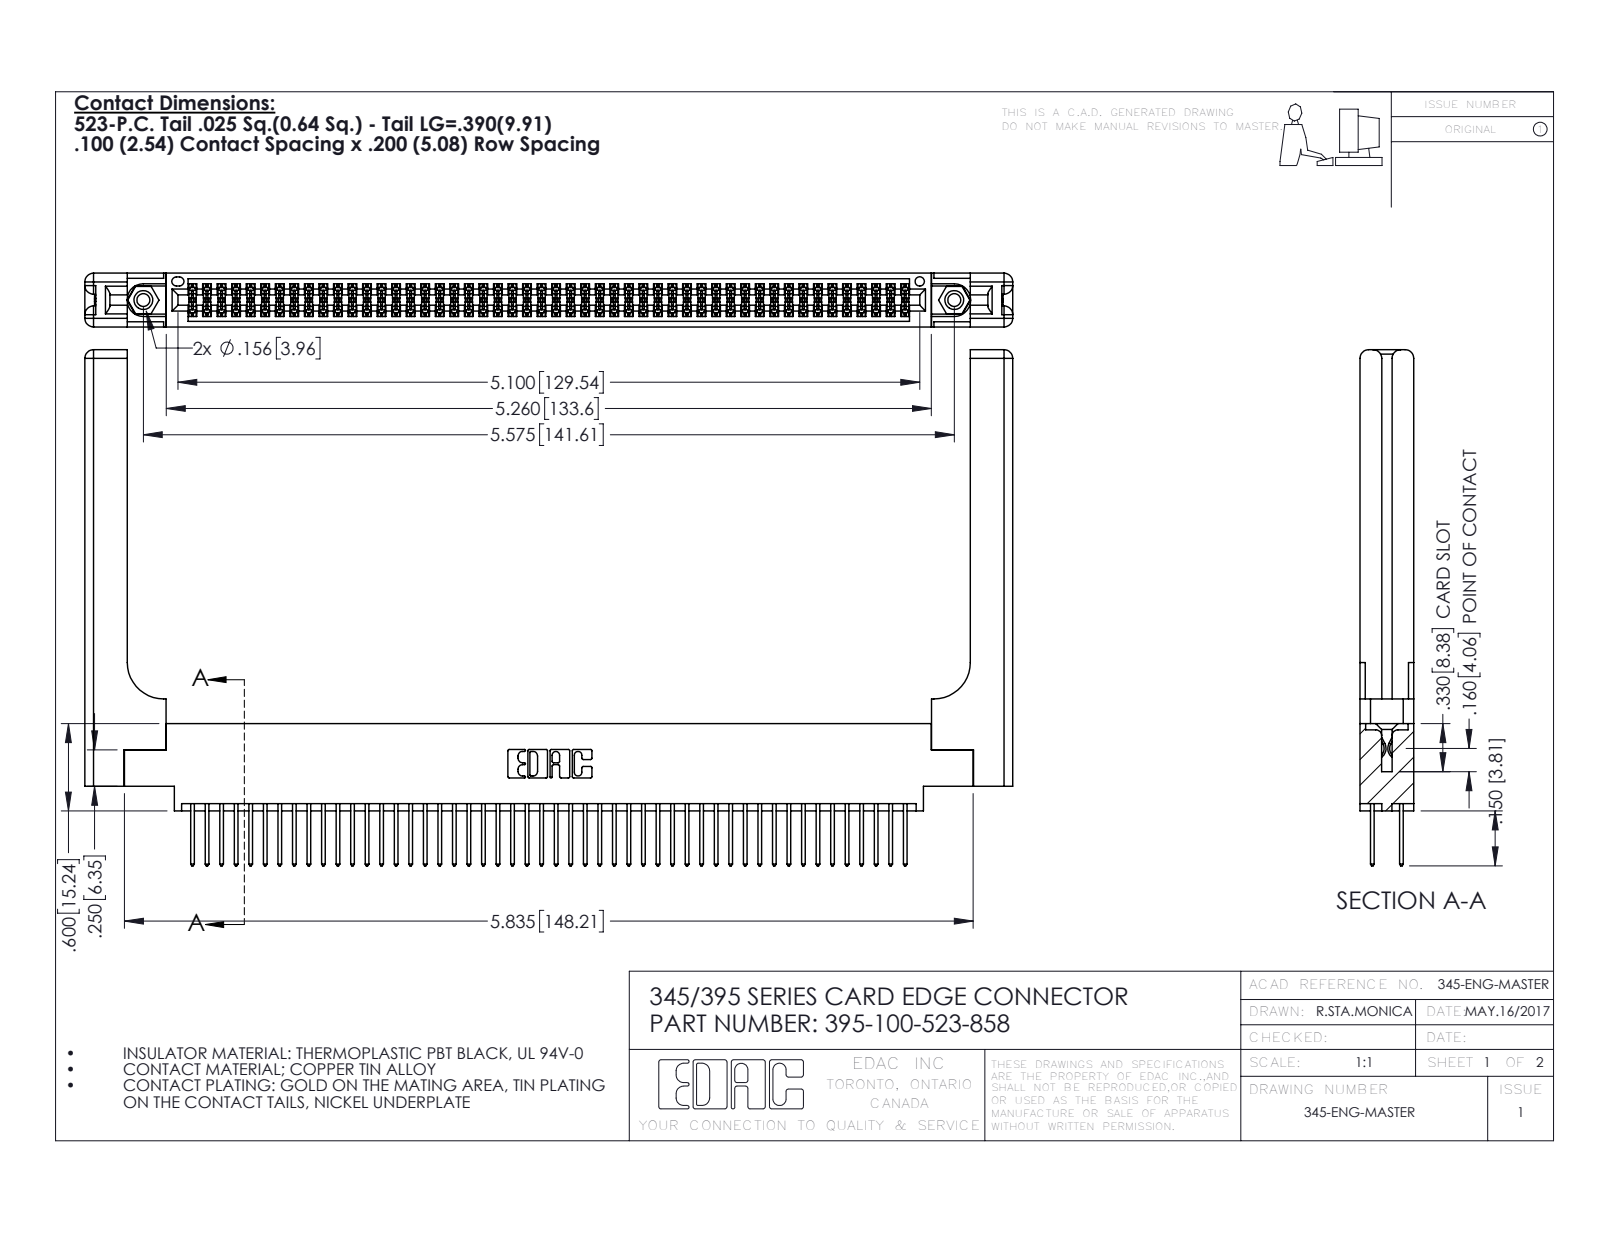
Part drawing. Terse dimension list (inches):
name: 345 Part_0.170 Offset - 0.156 Dia-TH; 395-100-523-858; 345-220-058_345-220-058; 345-292-001_345-293-123 (+1 more)
written by: SolidWorks 2016 (CONFIG_CONTROL_DESIGN)
unit: in
bodies: 105 solids, 5386 faces (3532 planar, 1794 cylindrical, 60 other)
size: 6.379 × 3.547 × 0.37
volume: 1.488 in³; area: 46.17 in²
holes: 2× ⌀0.089, 2× ⌀0.125, 2× ⌀0.156, 1× ⌀0.064
bosses: 2× ⌀0.155
rounds: 150× R0.006, 100× R0.01, 22× R0.01, 16× R0.06, 6× R0.007, 6× R0.031, 3× R0.026, 2× R0.014
face distances: 0.072, 0.298, 0.37, 0.098, 0.272, 0.025, 0.2, 0.225, 0.175, 0.148
hole spacings: 0.27, 5.339, 5.575
